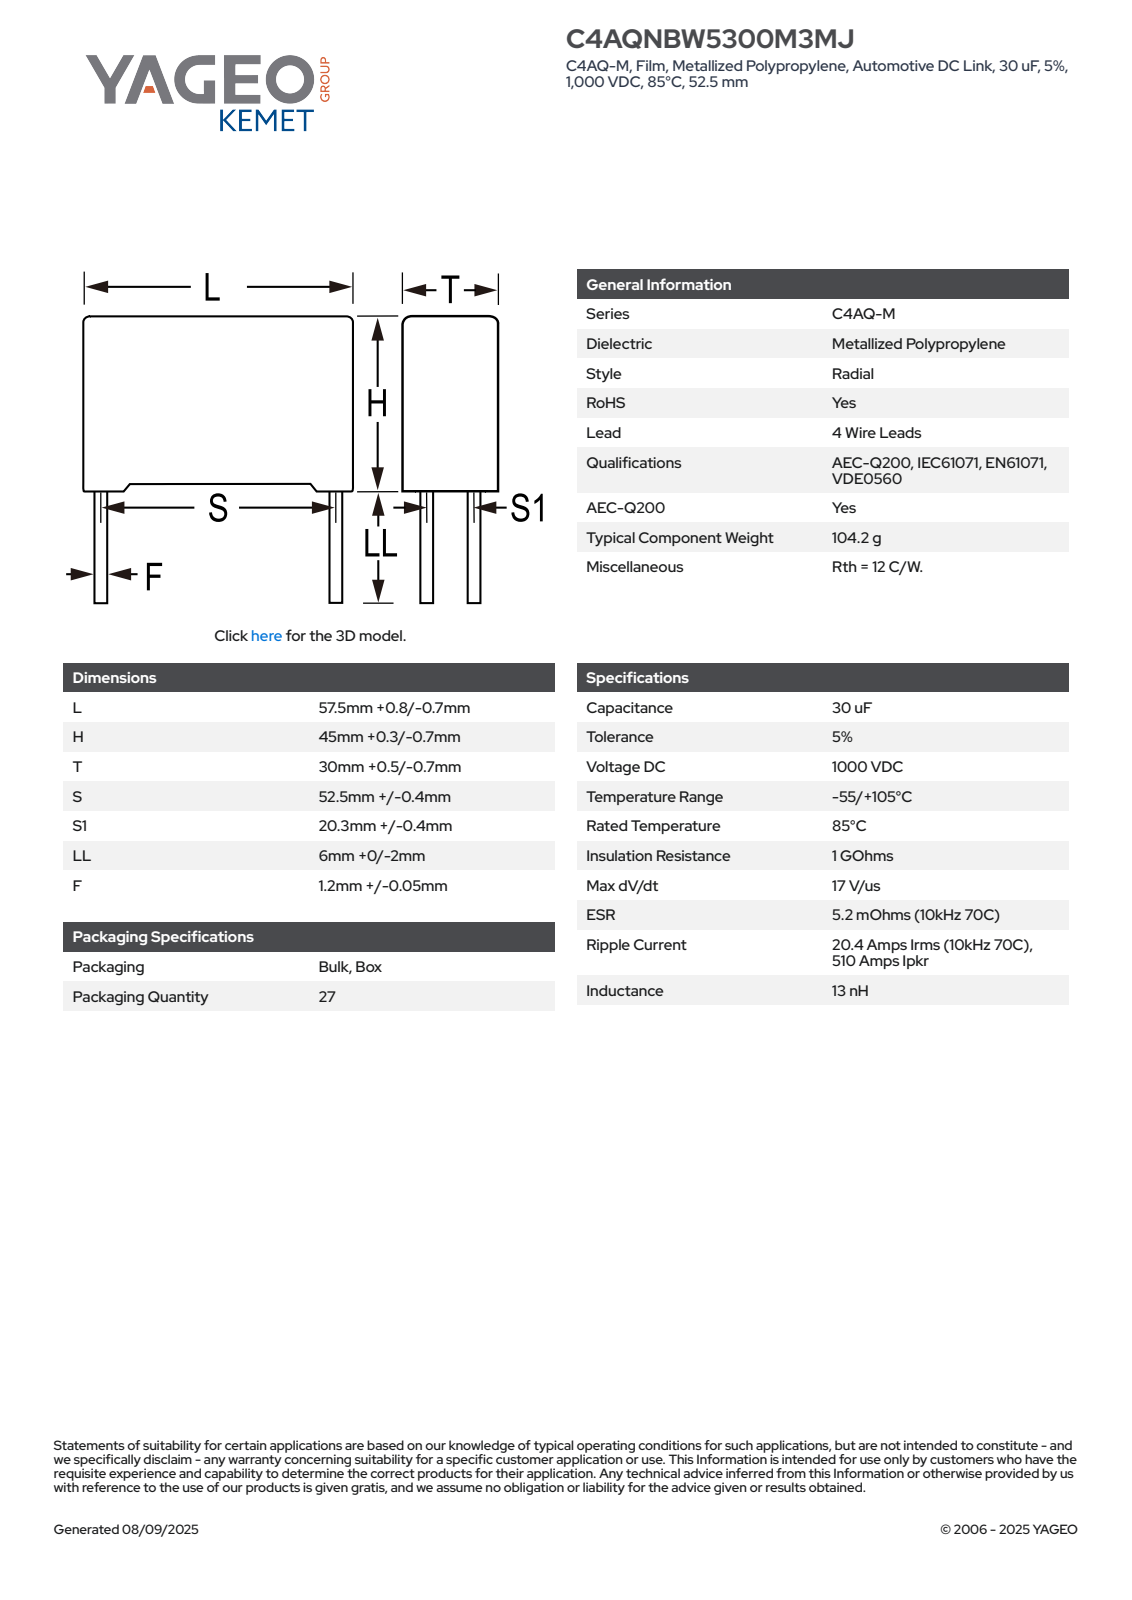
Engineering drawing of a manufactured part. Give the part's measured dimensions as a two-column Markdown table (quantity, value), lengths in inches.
| quantity | value |
| --- | --- |
| part name | CFP_RB4_57.5X45X30_L58.3H45.3T30.5S52.5S120.3LL6F1.25 |
| STEP written by | SolidWorks 2014 (AUTOMOTIVE_DESIGN) |
| units | inches |
| bodies | 4 solids, 87 faces (79 planar, 8 cylindrical, 0 other) |
| overall size | 2.295 × 2.02 × 1.201 |
| volume | 4.786 in³ |
| surface area | 18.49 in² |
| round bosses / shafts (diameter × count) | 0.049 × 4 |
| main face-to-face distances | 1.201, 1.731, 2.295, 0.052, 1.783, 1.201, 0.074, 2.222, 2.148, 1.127 |
